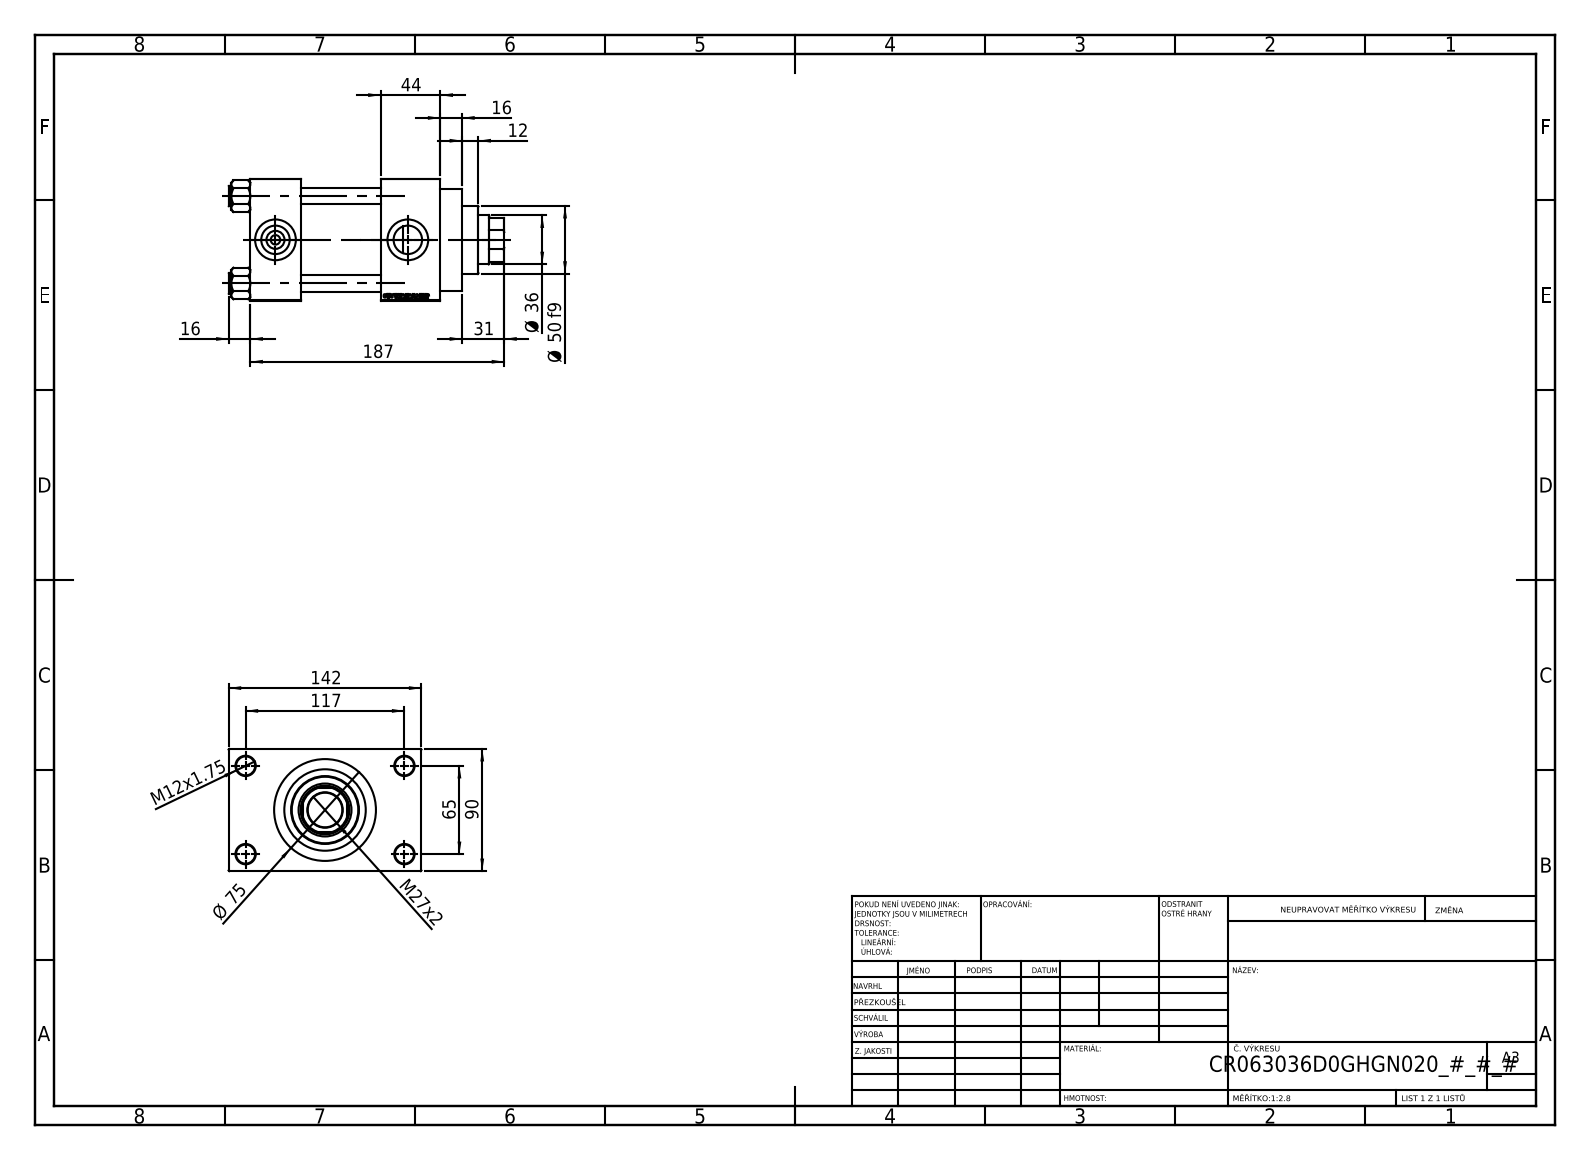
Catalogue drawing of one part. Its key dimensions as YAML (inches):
part_name: "V215CR_VCP_D; V215_VC_A; V215CR_D_TYCINKA; NUT_M5_D (+1 more)"
step_written_by: "SolidWorks 2019 (CONFIG_CONTROL_DESIGN)"
units: inches
bodies: {solids: 11, faces: 1103, planar: 497, cylindrical: 88, other: 518}
overall_size: [7.992, 5.591, 3.543]
volume: 67.86
surface_area: 319
round_holes:
  - {diameter: 0.472, count: 4}
  - {diameter: 0.551, count: 4}
  - {diameter: 0.276, count: 2}
  - {diameter: 0.825, count: 2}
  - {diameter: 1.181, count: 2}
  - {diameter: 1.004, count: 1}
  - {diameter: 1.417, count: 1}
  - {diameter: 1.535, count: 1}
  - {diameter: 1.969, count: 1}
  - {diameter: 2.362, count: 1}
  - {diameter: 2.48, count: 1}
round_bosses_or_shafts:
  - {diameter: 0.591, count: 4}
  - {diameter: 2.953, count: 1}
  - {diameter: 2.717, count: 1}
partial_cylinders:
  - {radius: 0.689, count: 1}
face_to_face_distances: [3.543, 2.323, 1.457, 3.78, 5.512, 4.055, 1.732, 1.024, 4.567, 5.591]
hole_center_spacings: [1.037, 1.79, 2.531, 2.635, 2.748, 3.569, 4.383, 2.559]
